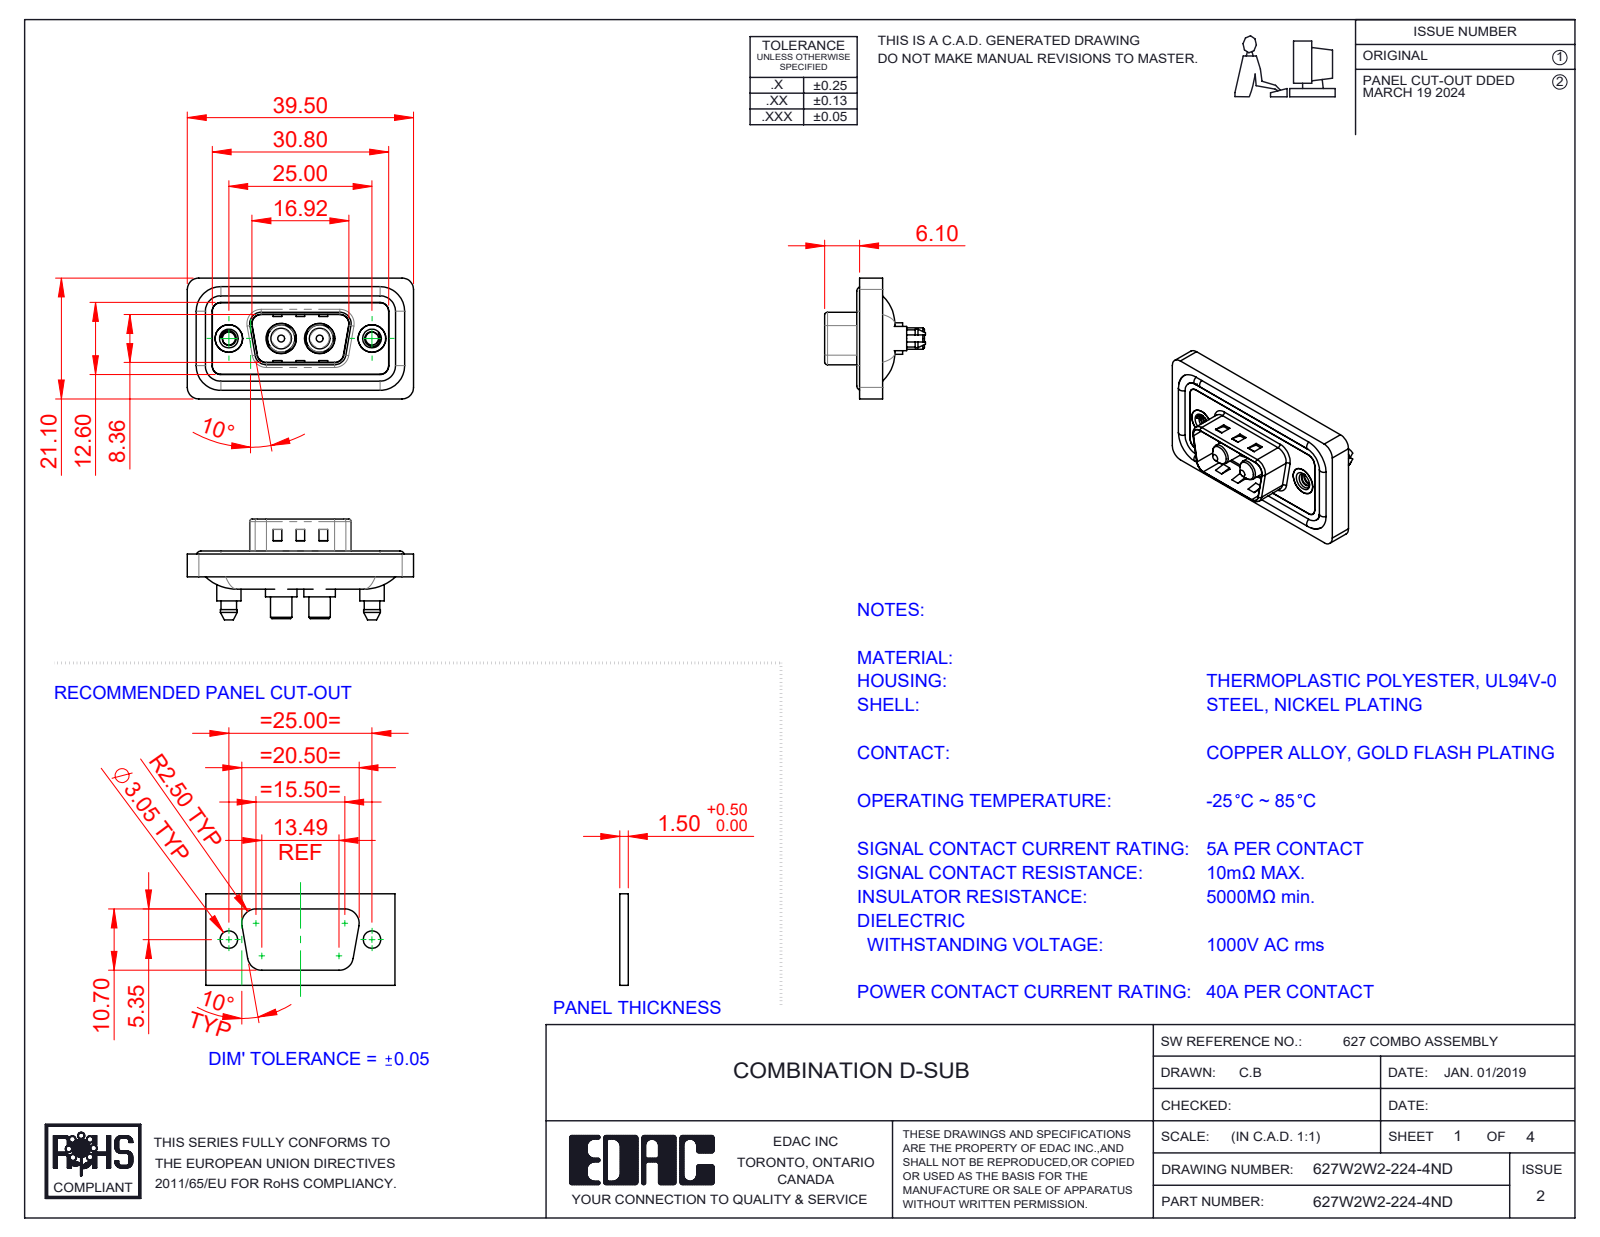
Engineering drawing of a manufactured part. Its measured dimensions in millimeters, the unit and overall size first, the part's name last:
Units: millimetres
Overall size (bounding box): 39.5 × 21.1 × 17.6
Round holes (diameter × count): ⌀2.26 ×2, ⌀4 ×2, ⌀4.8 ×2, ⌀4.85 ×2, ⌀5 ×2, ⌀5.3 ×2
Round bosses / shafts (diameter × count): ⌀1.6 ×4, ⌀5.5 ×2, ⌀5.4 ×2, ⌀5.2 ×2, ⌀4.9 ×2, ⌀4.75 ×2, ⌀4.25 ×2, ⌀3.75 ×2
Partial cylindrical surfaces — rounded edges, fillets, slot ends (radius × count): R1.5 ×24, R2 ×18, R1.6 ×10, R0.5 ×8, R0.25 ×4, R0.6 ×4, R0.65 ×4, R0.9 ×4
Main face-to-face distances: 0.4, 1.1, 2.9, 3.1, 0.5, 1.6, 1.5, 4, 0.7, 2.5
Hole centre spacings: 9.14, 15.86, 6.72, 25
Volume: 4 632 mm³ · Surface area: 7 342 mm²
Bodies: 11 solids, 547 faces (181 planar, 258 cylindrical, 108 other)
Part name (STEP PRODUCT): 627Combo Shell Front_09 Contacts; Power Pin_40A S; 627Combo Waterproof Housing_09 Contacts; 627Combo Shell Rear_09 Contacts (+4 more)
STEP written by: SolidWorks 2023 (CONFIG_CONTROL_DESIGN)
